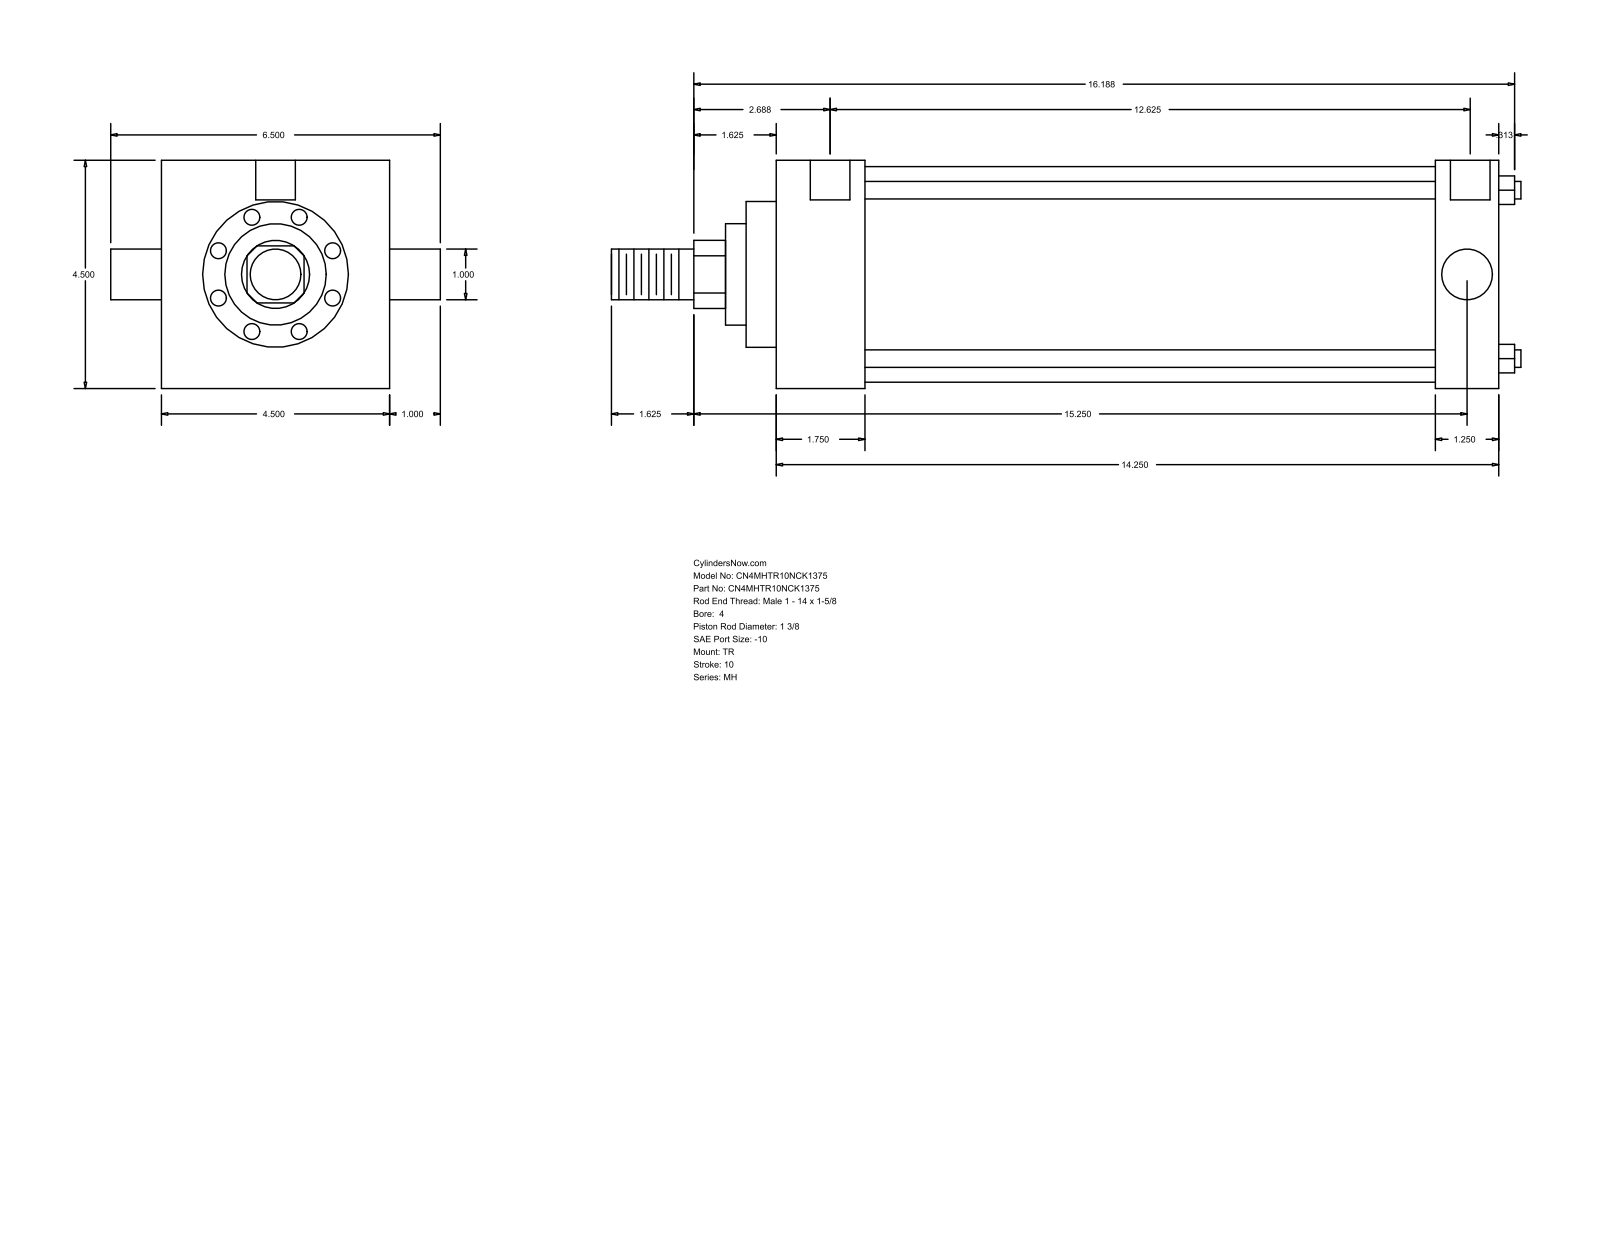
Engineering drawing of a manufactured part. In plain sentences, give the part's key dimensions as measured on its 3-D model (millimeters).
The part is named "MH_TR__0400_1.375". Its 3-D file was written by "GSSL Pune (CONFIG_CONTROL_DESIGN)". It is 0 solids with 86 faces: 61 planar, 25 cylindrical and 0 other. Overall it measures 455.61 by 165.1 by 114.3 millimeters. Round holes: 3 of diameter 8.73, 2 of diameter 19.84. Round bosses or shafts: 4 of diameter 8.76, 2 of diameter 25.4, 1 of diameter 107.95, 1 of diameter 73.03, 1 of diameter 50.8, 1 of diameter 34.92. Partial cylindrical surfaces (rounded edges, fillets, slot ends): 1 of radius 17.06. The main face-to-face distances are 114.3, 361.96, 44.45, 317.51, 330.21, 285.76, 31.75, 15.08, 59.53, 345.29. The hole center spacings are 1.58, 1.59, 320.68, 322.26, 322.27, 323.85.
